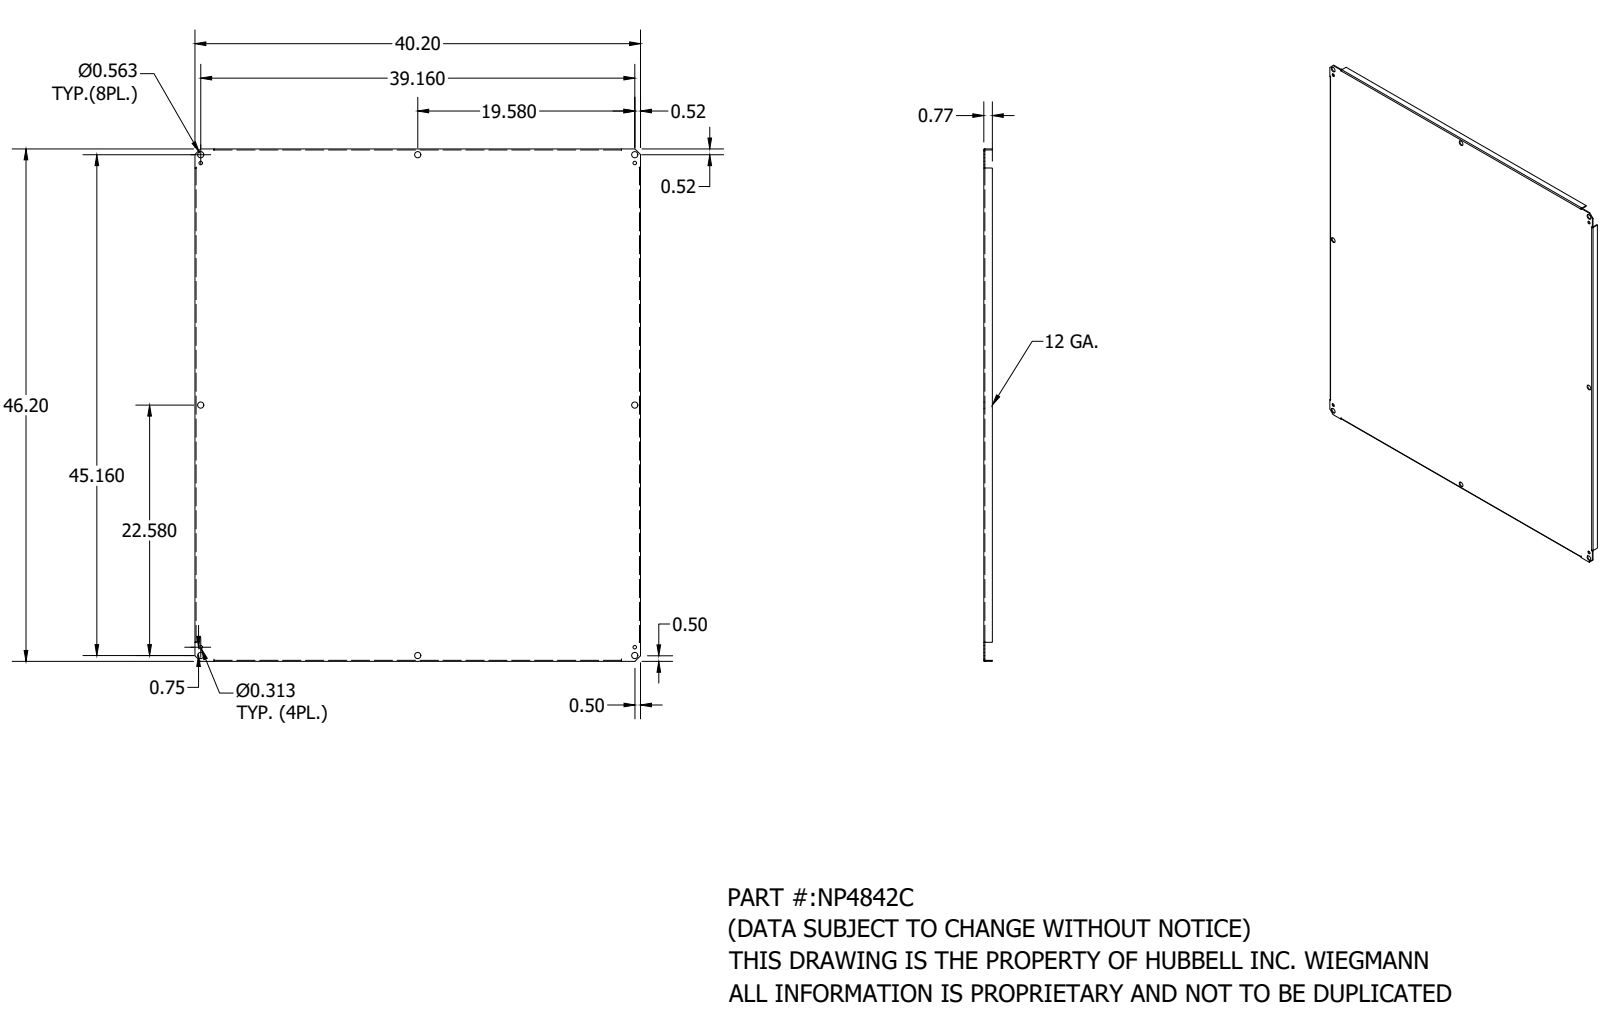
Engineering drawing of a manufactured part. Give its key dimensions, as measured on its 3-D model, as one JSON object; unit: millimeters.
{"part_name": "NP4842C", "step_written_by": "Autodesk Inventor 2018 (AUTOMOTIVE_DESIGN)", "units": "millimeters", "bodies": {"solids": 1, "faces": 70, "planar": 50, "cylindrical": 20, "other": 0}, "overall_size": [1173.5, 1021.1, 19.7], "volume_mm3": 3009000, "surface_area_mm2": 2539000, "round_holes": [[14.3, 8], [8, 4]], "partial_cylinders_radius": [[0.4, 4], [2.8, 4]], "face_to_face_distances": [2.4, 1018.7, 1171.1, 1021.1, 1016.3, 1173.5, 1168.7, 17.3, 19.7, 43.6], "hole_center_spacings": [994.7, 19.1, 497.3, 497.7, 554.5, 573.5, 759.1, 994.8]}
